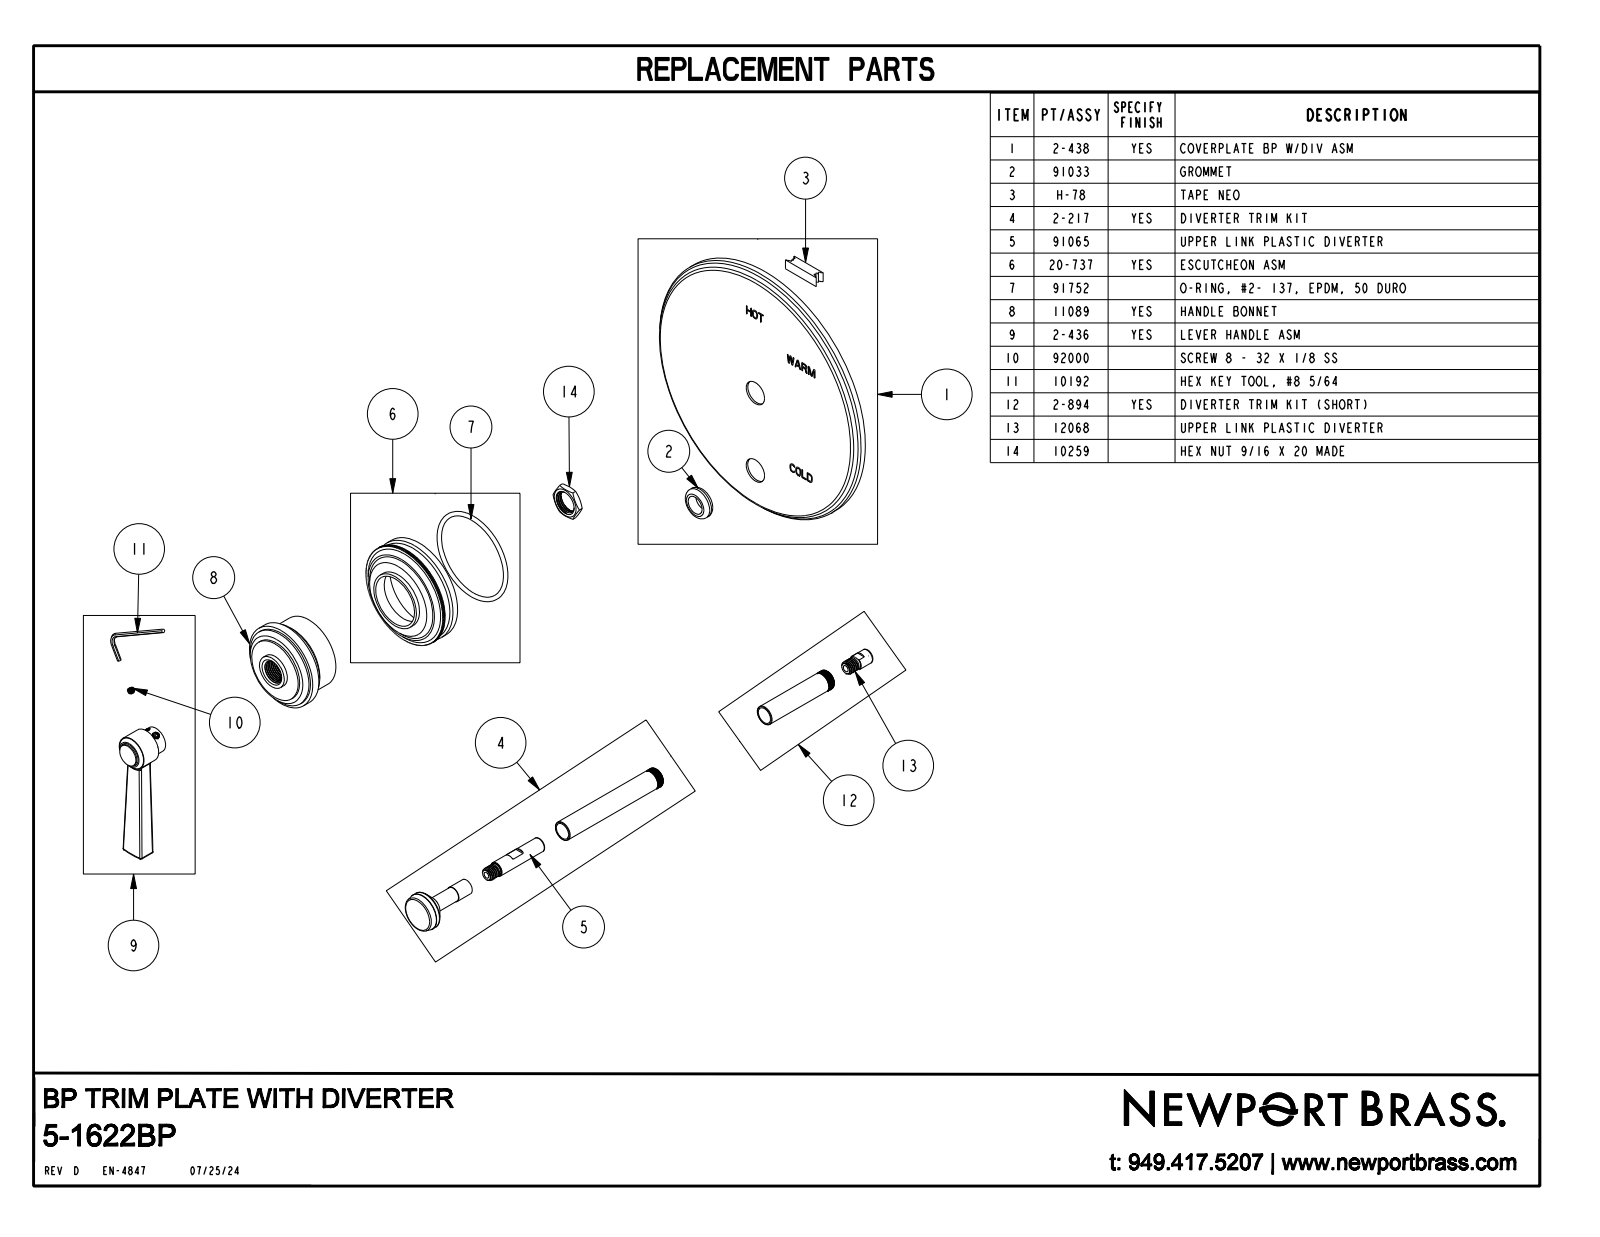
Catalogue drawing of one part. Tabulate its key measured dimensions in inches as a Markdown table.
| quantity | value |
| --- | --- |
| part name | 5-1622BP |
| STEP written by | CREO PARAMETRIC BY PTC INC, 2018400 (CONFIG_CONTROL_DESIGN) |
| units | inches |
| bodies | 1 solid, 920 faces (642 planar, 216 cylindrical, 62 other) |
| overall size | 6.5 × 6.5 × 3.131 |
| volume | 17.22 in³ |
| surface area | 93.88 in² |
| round bosses / shafts (diameter × count) | 6.5 × 1, 2.5 × 1, 2.4 × 1, 2.05 × 1, 1.9 × 1, 1.75 × 1, 1.5 × 1, 0.9 × 1 |
| partial cylindrical surfaces (radius × count) | 0.04 × 2, 0.055 × 2 |
| main face-to-face distances | 0.313, 2.088, 1.775, 0.2, 0.1, 1.3, 0.15, 0.4, 1.375, 0.9 |
